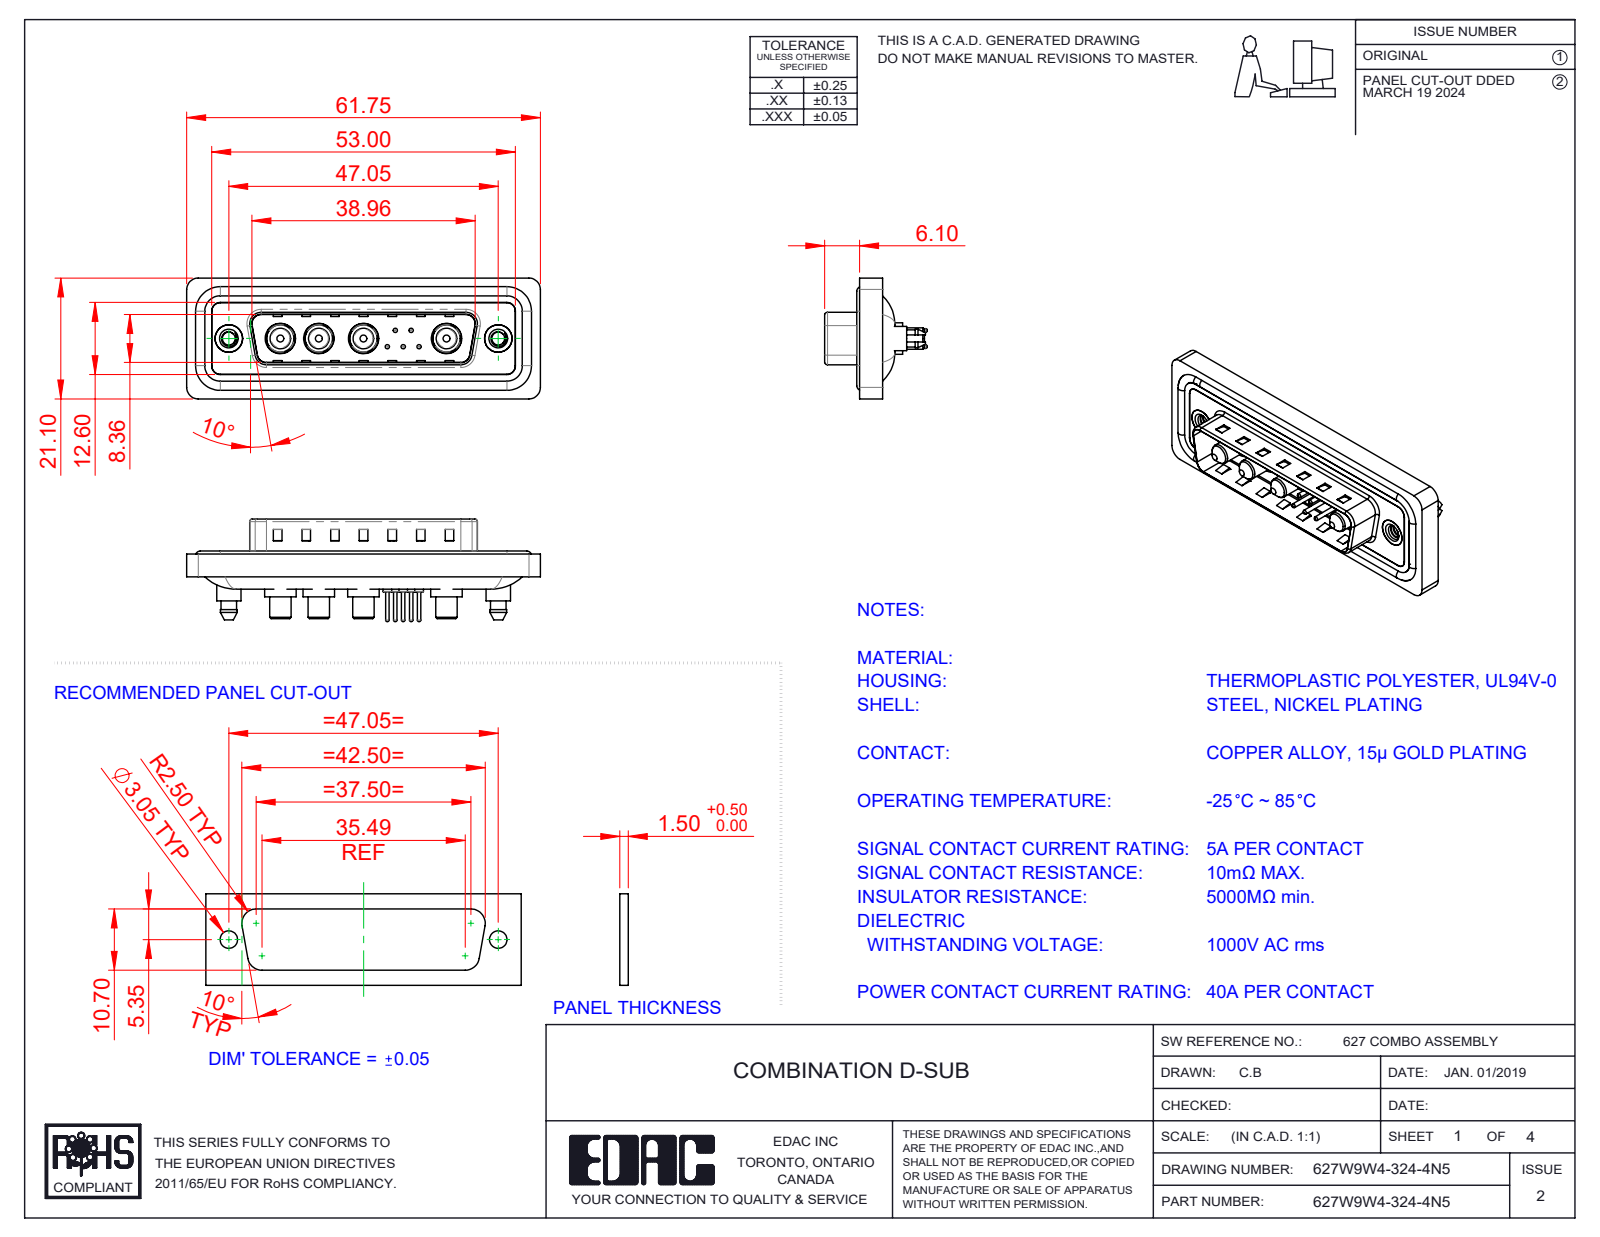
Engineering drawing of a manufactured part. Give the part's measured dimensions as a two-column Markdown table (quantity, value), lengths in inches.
| quantity | value |
| --- | --- |
| part name | 627Combo Shell Rear_25 Contacts; Power Pin_40A S; 627Combo Threaded Boardlock_5; 627Combo Contact Row 1_24 (+5 more) |
| STEP written by | SolidWorks 2023 (CONFIG_CONTROL_DESIGN) |
| units | inches |
| bodies | 20 solids, 874 faces (300 planar, 366 cylindrical, 208 other) |
| overall size | 2.431 × 0.831 × 0.705 |
| volume | 0.465 in³ |
| surface area | 18.93 in² |
| round holes (diameter × count) | 0.03 × 5, 0.063 × 5, 0.079 × 5, 0.191 × 4, 0.209 × 4, 0.089 × 2, 0.157 × 2, 0.189 × 2, 0.197 × 2 |
| round bosses / shafts (diameter × count) | 0.059 × 5, 0.024 × 5, 0.217 × 4, 0.205 × 4, 0.187 × 4, 0.148 × 4, 0.142 × 4, 0.063 × 4 |
| partial cylindrical surfaces (radius × count) | 0.059 × 24, 0.079 × 18, 0.063 × 10, 0.02 × 8, 0.01 × 4, 0.024 × 4, 0.026 × 4, 0.035 × 4 |
| main face-to-face distances | 0.016, 0.059, 0.043, 0.02, 0.122, 0.063, 0.114, 0.032, 0.377, 0.222 |
| hole center spacings | 0.124, 0.109, 0.198, 0.571, 0.109, 0.173, 0.174, 0.197 |
